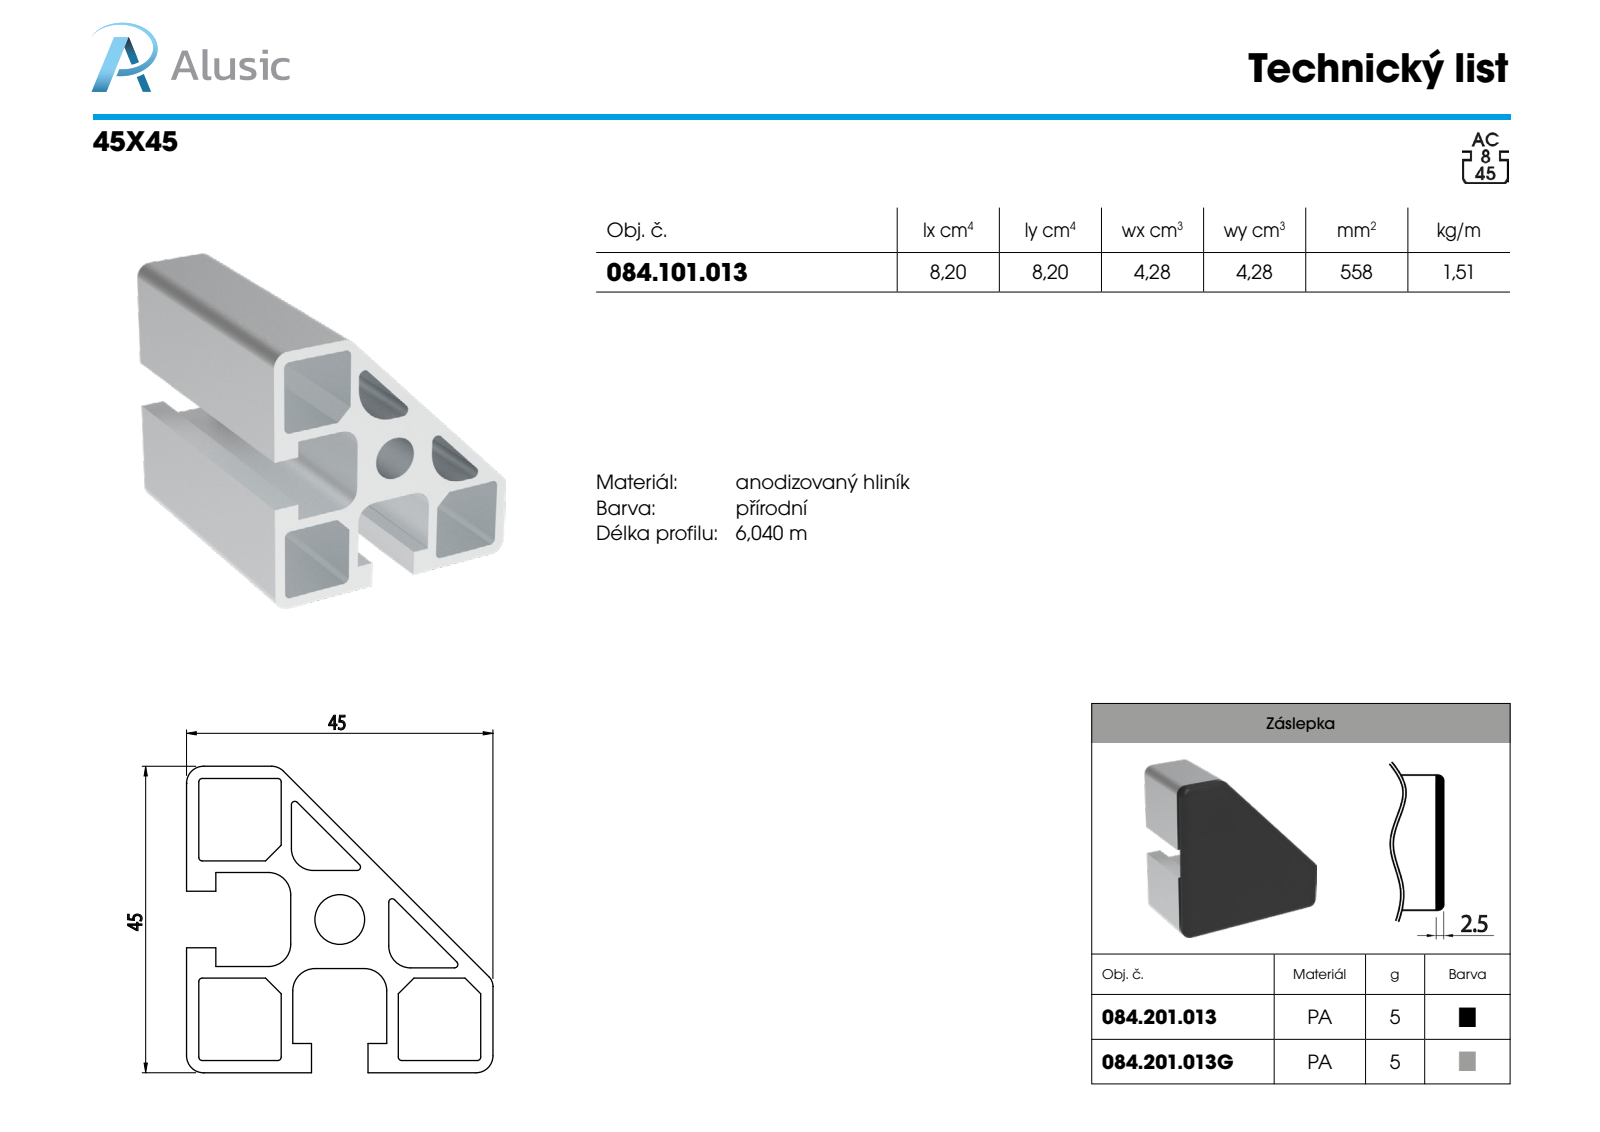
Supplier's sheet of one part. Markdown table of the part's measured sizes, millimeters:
| quantity | value |
| --- | --- |
| part name | 084.101.013 |
| STEP written by | SolidWorks 2018 (AUTOMOTIVE_DESIGN) |
| units | millimeters |
| bodies | 1 solid, 72 faces (44 planar, 28 cylindrical, 0 other) |
| overall size | 100 × 45 × 45 |
| volume | 59 093 mm³ |
| surface area | 46 692 mm² |
| round holes (diameter × count) | 7.3 × 1 |
| partial cylindrical surfaces (radius × count) | 1 × 13, 2.5 × 5, 3 × 4, 6.4 × 2 |
| main face-to-face distances | 1.8, 13.9, 12.1, 13.8, 43.2, 29.3, 31.1, 27.6, 15.6, 29.4 |
